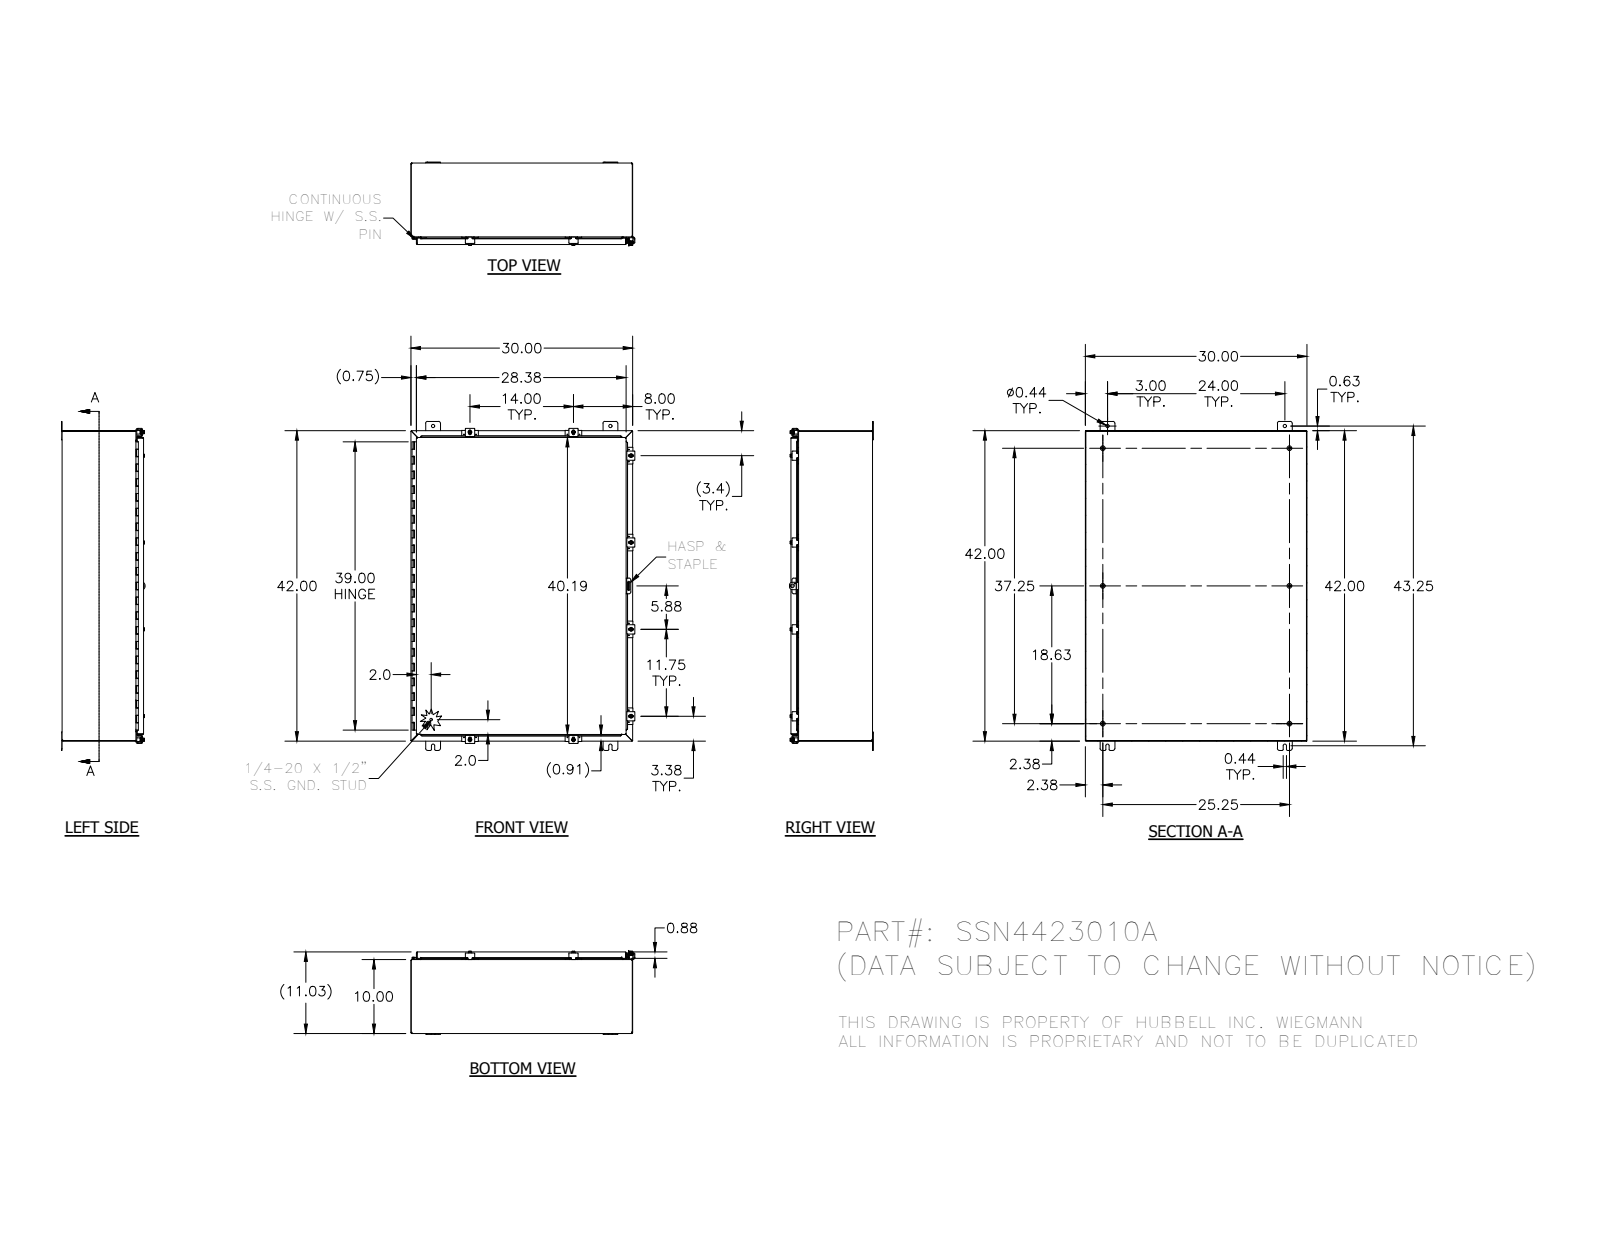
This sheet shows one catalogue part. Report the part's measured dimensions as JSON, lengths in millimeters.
{"part_name": "38412; SSN4423010A; 38859; 30824 (+8 more)", "step_written_by": "SolidWorks 2014 (AUTOMOTIVE_DESIGN)", "units": "millimeters", "bodies": {"solids": 59, "faces": 2430, "planar": 959, "cylindrical": 1058, "other": 413}, "overall_size": [1130.3, 767.5, 288.4], "volume_mm3": 5613000, "surface_area_mm2": 5844000, "round_holes": [[2.8, 16], [5.4, 8], [7.1, 8], [7.6, 8], [11.1, 4], [3.2, 1], [4, 1], [12.7, 1]], "round_bosses_or_shafts": [[6.4, 10], [13.2, 8], [12.7, 8], [8.9, 8], [15.9, 6], [8.4, 6], [8.6, 1], [3, 1]], "partial_cylinders_radius": [[0.8, 95], [3.2, 39], [6.4, 35], [0.8, 23], [2.7, 23], [1.6, 20], [3.6, 16], [2.5, 12]], "face_to_face_distances": [1.9, 278.4, 276.5, 280.2, 760.1, 1064.9, 762, 758.2, 252.1, 26.2], "hole_center_spacings": [22.3, 298.5, 1048.9, 355.6, 596.9, 22.3, 41.3, 41.3]}
